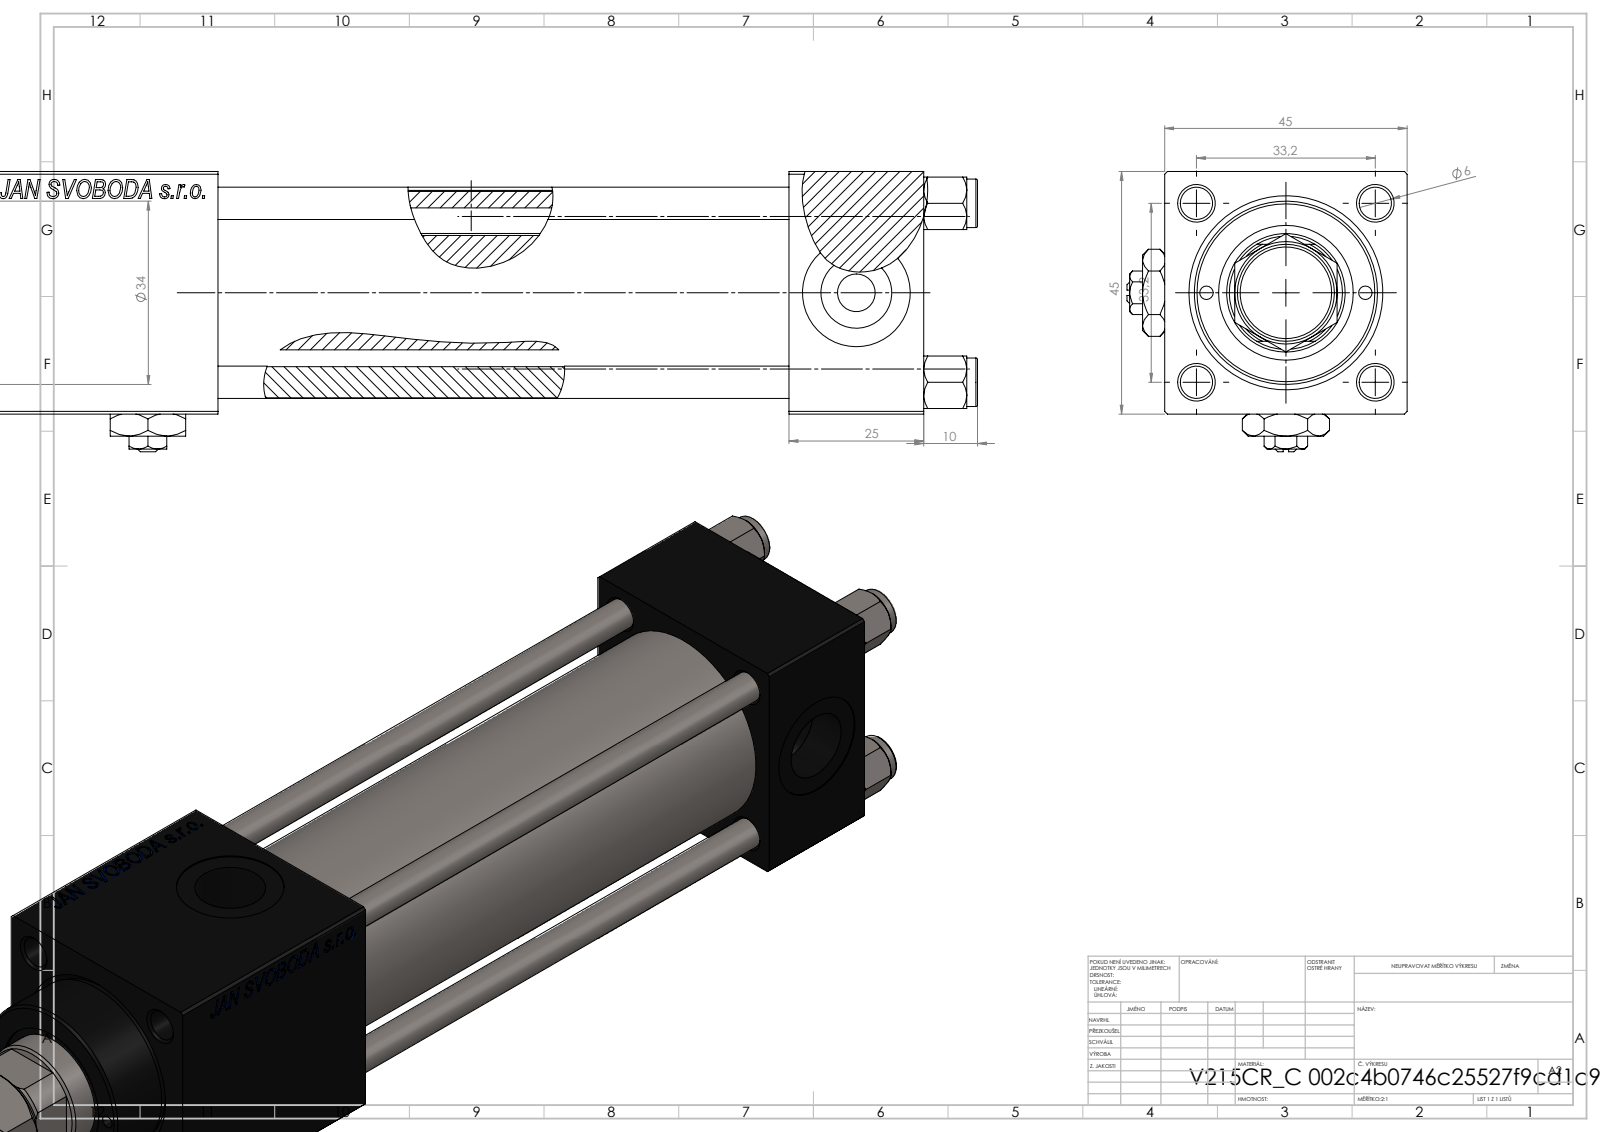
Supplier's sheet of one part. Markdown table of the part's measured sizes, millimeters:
| quantity | value |
| --- | --- |
| part name | NUT_M5_C; V215CR_VCP_C; MFA; V215CR_C_TYCINKA (+3 more) |
| STEP written by | SolidWorks 2019 (CONFIG_CONTROL_DESIGN) |
| units | millimeters |
| bodies | 13 solids, 1306 faces (590 planar, 106 cylindrical, 610 other) |
| overall size | 247 × 52 × 52 |
| volume | 126 687 mm³ |
| surface area | 96 517 mm² |
| round holes (diameter × count) | 6 × 4, 2.5 × 2, 7 × 2, 13.16 × 2, 20 × 2, 10.5 × 1, 22 × 1, 24 × 1, 25 × 1, 32 × 1, 33 × 1 |
| round bosses / shafts (diameter × count) | 9 × 4, 38 × 1, 34 × 1, 18 × 1, 11 × 1 |
| partial cylindrical surfaces (radius × count) | 10.5 × 1 |
| main face-to-face distances | 45, 25, 179, 106, 131, 154, 44.8, 13, 48, 150.3 |
| hole center spacings | 16.7, 23.48, 33.2, 35.47, 14.75, 46.95, 29.5 |
